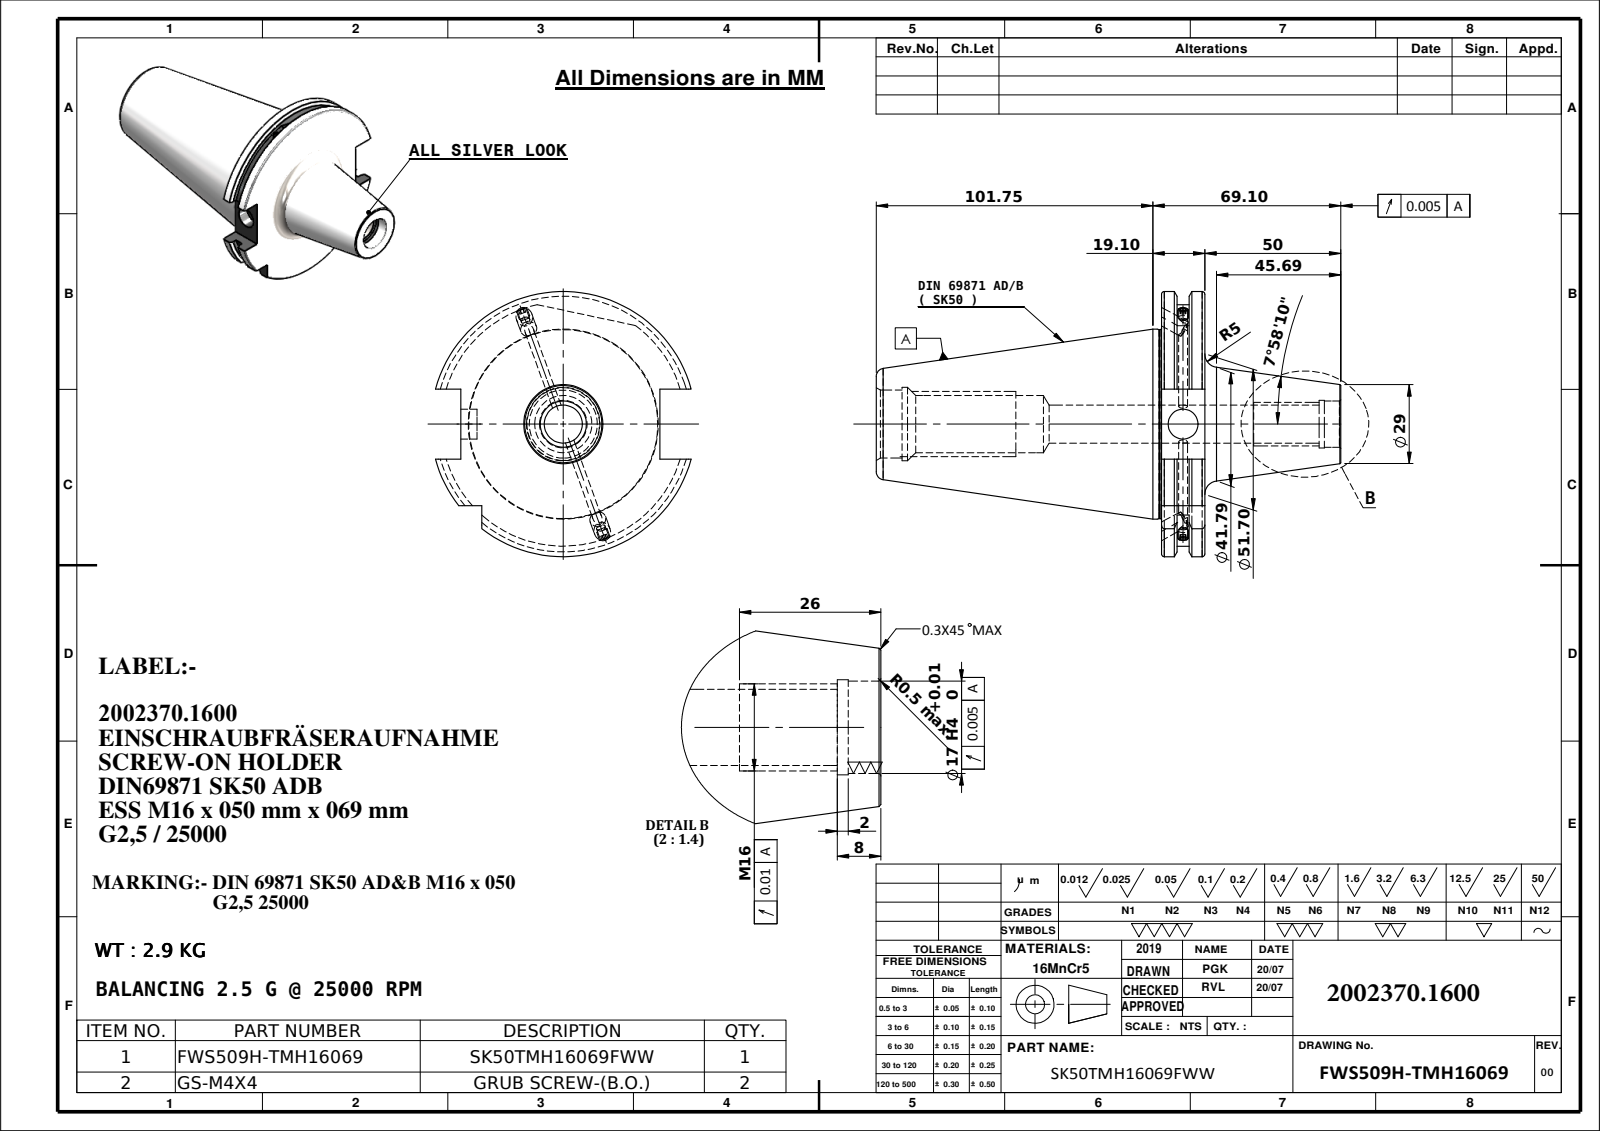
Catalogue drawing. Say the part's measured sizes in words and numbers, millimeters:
The part is named "91506-ES7M16050". Its 3-D file was written by "SolidWorks 2018 (CONFIG_CONTROL_DESIGN)". It is 1 solid with 108 faces: 25 planar, 43 cylindrical and 40 other. Overall it measures 170.85 by 97.5 by 94.05 millimeters. Its volume is 372 635 cubic millimeters and its surface area 50 915 square millimeters. Round holes: 2 of diameter 6, 1 of diameter 3.3, 1 of diameter 11, 1 of diameter 14, 1 of diameter 17, 1 of diameter 17.5, 1 of diameter 21, 1 of diameter 25, 1 of diameter 27. Round bosses or shafts: 1 of diameter 69.85, 1 of diameter 69.45. Partial cylindrical surfaces (rounded edges, fillets, slot ends): 1 of radius 44.9, 1 of radius 48.75. The main face-to-face distances are 15.9, 5.66, 10.24, 10.14, 4.48, 5.76, 104.95, 110.61, 115.09, 120.85.
